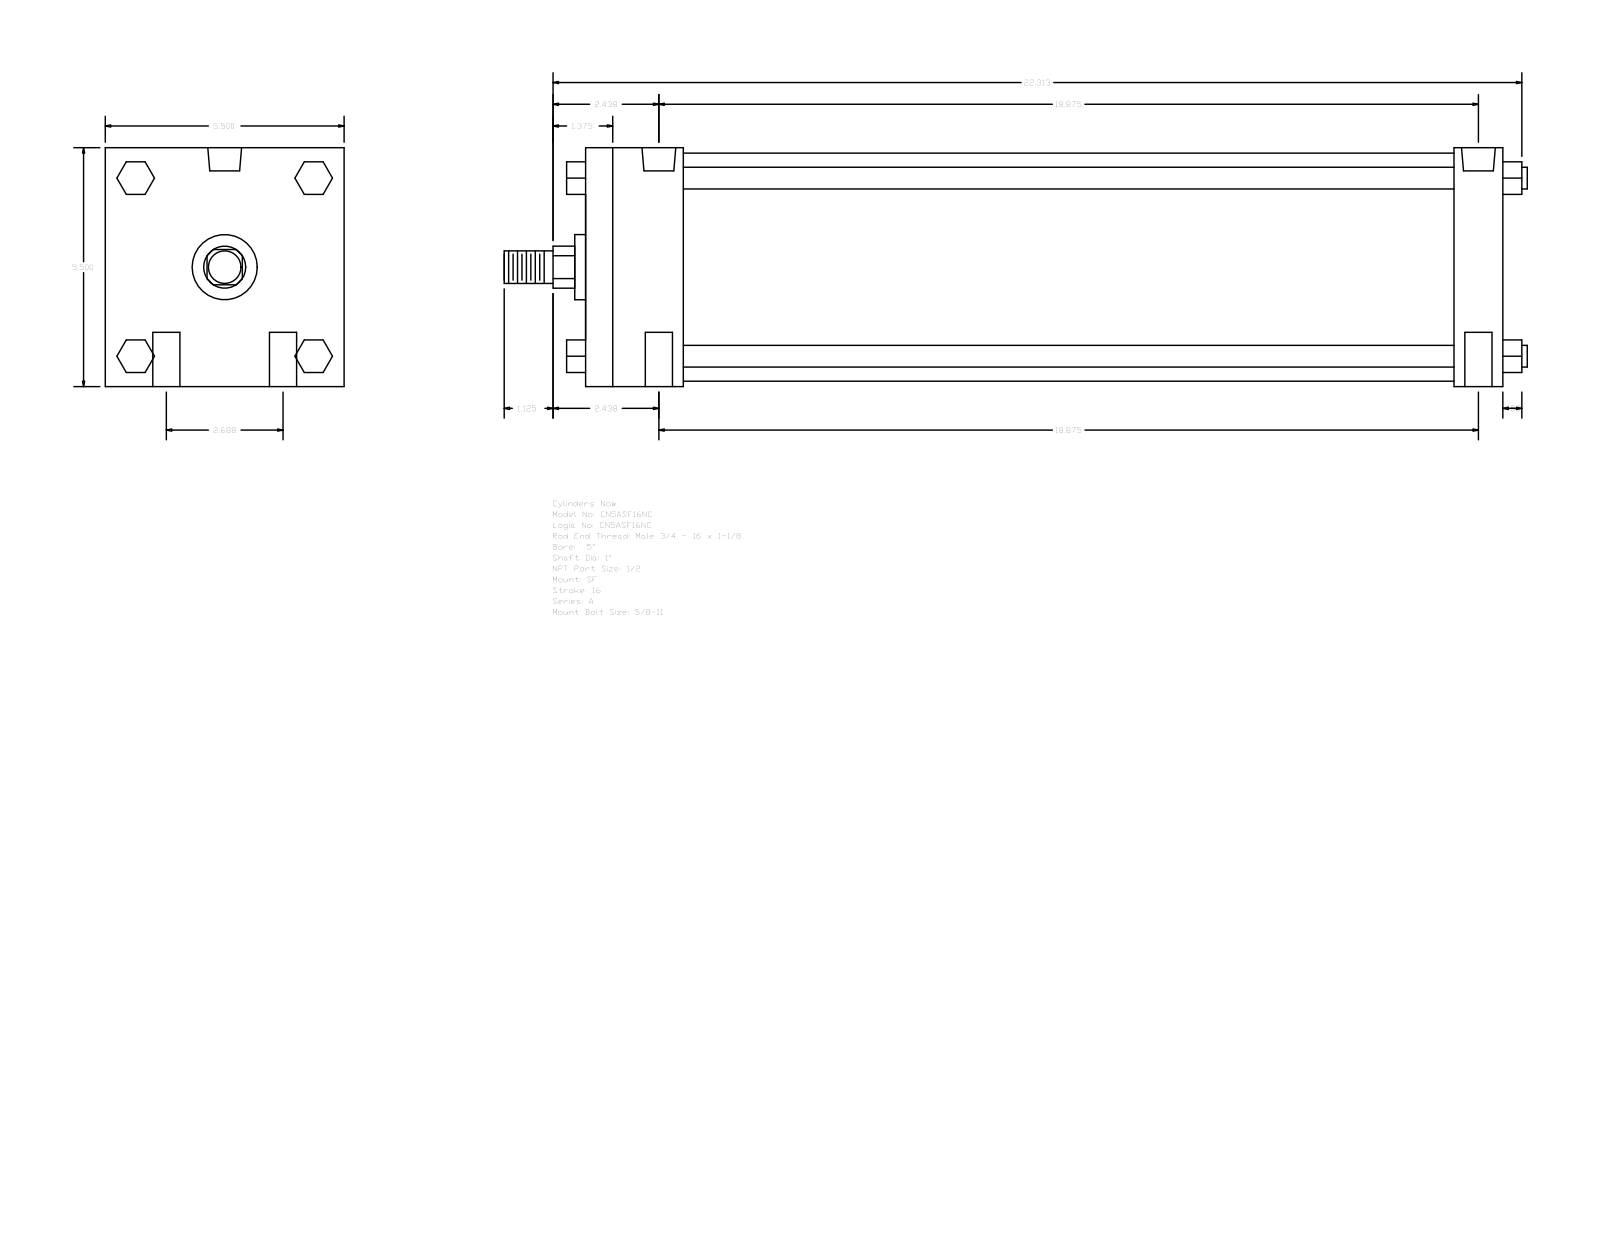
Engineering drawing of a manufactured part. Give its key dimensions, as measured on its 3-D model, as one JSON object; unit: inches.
{"part_name": "A_SF__0500_1", "step_written_by": "GSSL Pune (CONFIG_CONTROL_DESIGN)", "units": "inches", "bodies": {"solids": 0, "faces": 124, "planar": 94, "cylindrical": 30, "other": 0}, "overall_size": [23.563, 5.5, 5.5], "round_holes": [[0.625, 4], [0.344, 2], [0.778, 2]], "round_bosses_or_shafts": [[0.5, 4], [5.25, 1], [1.5, 1], [1, 1], [0.75, 1]], "partial_cylinders_radius": [[0.484, 1]], "face_to_face_distances": [5.5, 21.125, 1.125, 2.25, 20, 17.75, 18.875, 0.75, 2.05, 3.55], "hole_center_spacings": [1.344, 18.923, 18.875, 2.687, 19.065, 18.687]}
